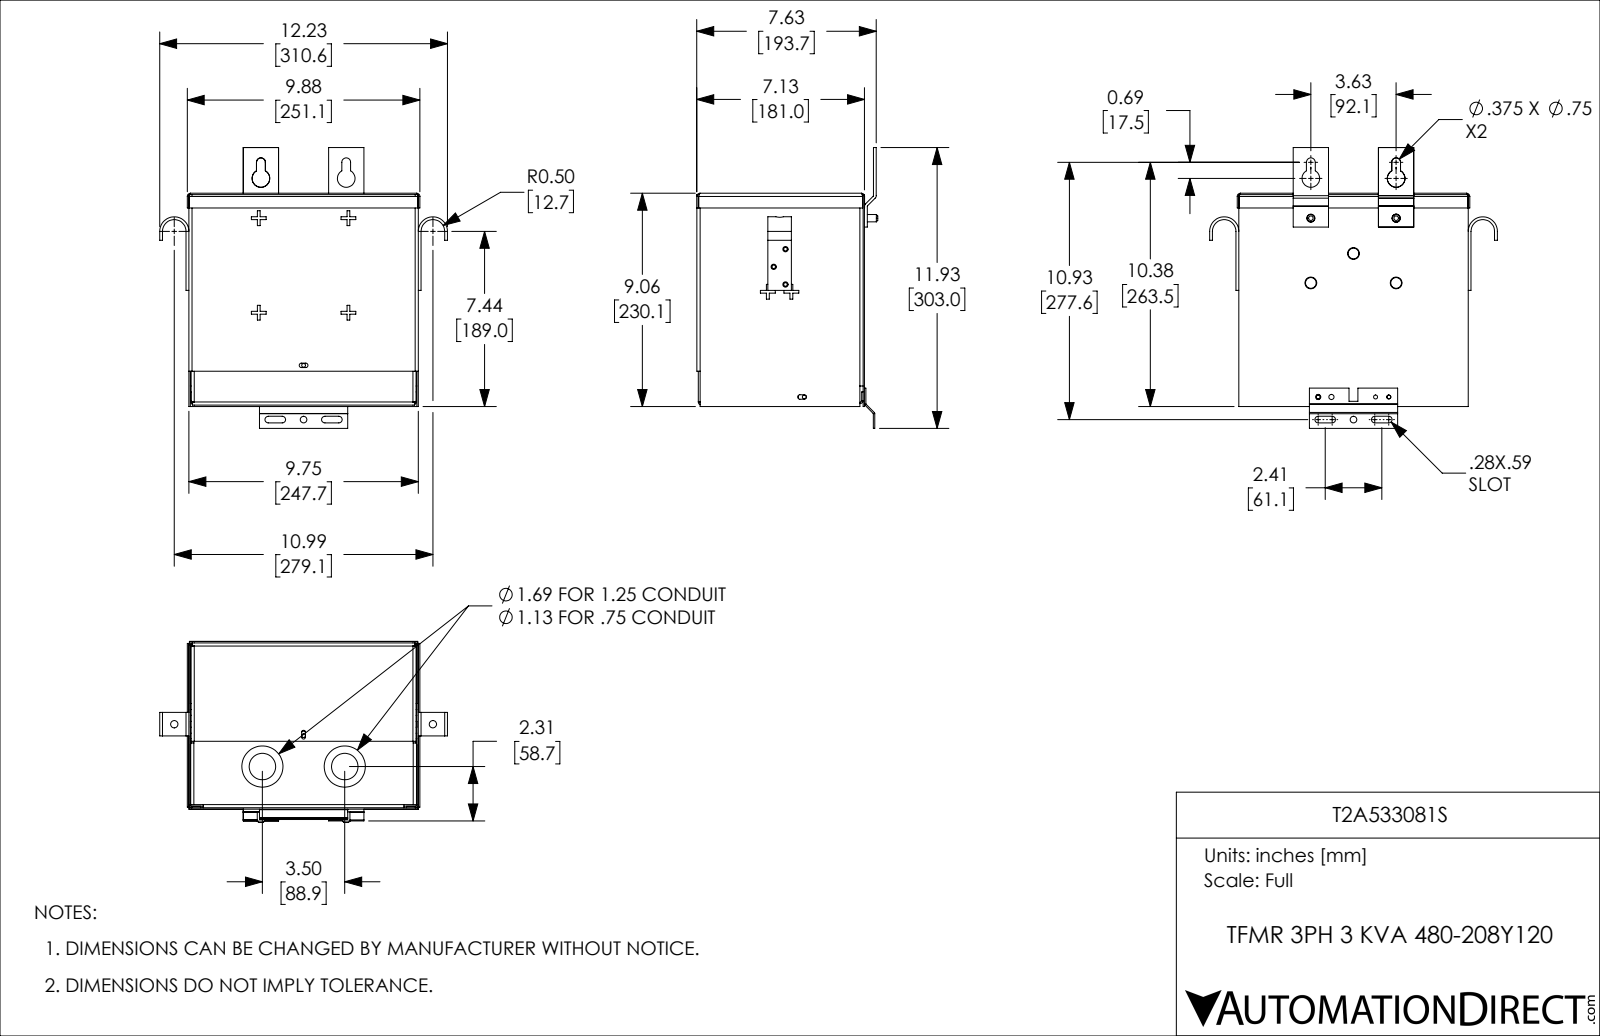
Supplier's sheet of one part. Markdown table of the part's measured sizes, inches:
| quantity | value |
| --- | --- |
| part name | T2A533081S |
| STEP written by | SolidWorks 2017 (AUTOMOTIVE_DESIGN) |
| units | inches |
| bodies | 9 solids, 621 faces (405 planar, 144 cylindrical, 72 other) |
| overall size | 12.23 × 11.929 × 7.693 |
| volume | 31.98 in³ |
| surface area | 1 026 in² |
| round holes (diameter × count) | 0.16 × 5, 0.172 × 2, 0.219 × 2, 0.281 × 2, 0.313 × 2, 0.344 × 2, 0.75 × 2, 1.125 × 2, 1.75 × 2, 0.173 × 1, 0.187 × 1 |
| round bosses / shafts (diameter × count) | 1.87 × 2, 1.245 × 2, 0.312 × 2 |
| partial cylindrical surfaces (radius × count) | 0.075 × 16, 0.135 × 16, 0.094 × 8, 0.141 × 4, 0.02 × 2, 0.03 × 2, 0.078 × 2, 0.08 × 2 |
| main face-to-face distances | 0.06, 7.062, 0.059, 7.002, 8.94, 7.122, 9.69, 9.691, 9.75, 9.631 |
| hole center spacings | 0.563, 1.342, 1.638, 1.687, 1.781, 2.014, 2.187, 2.437 |
